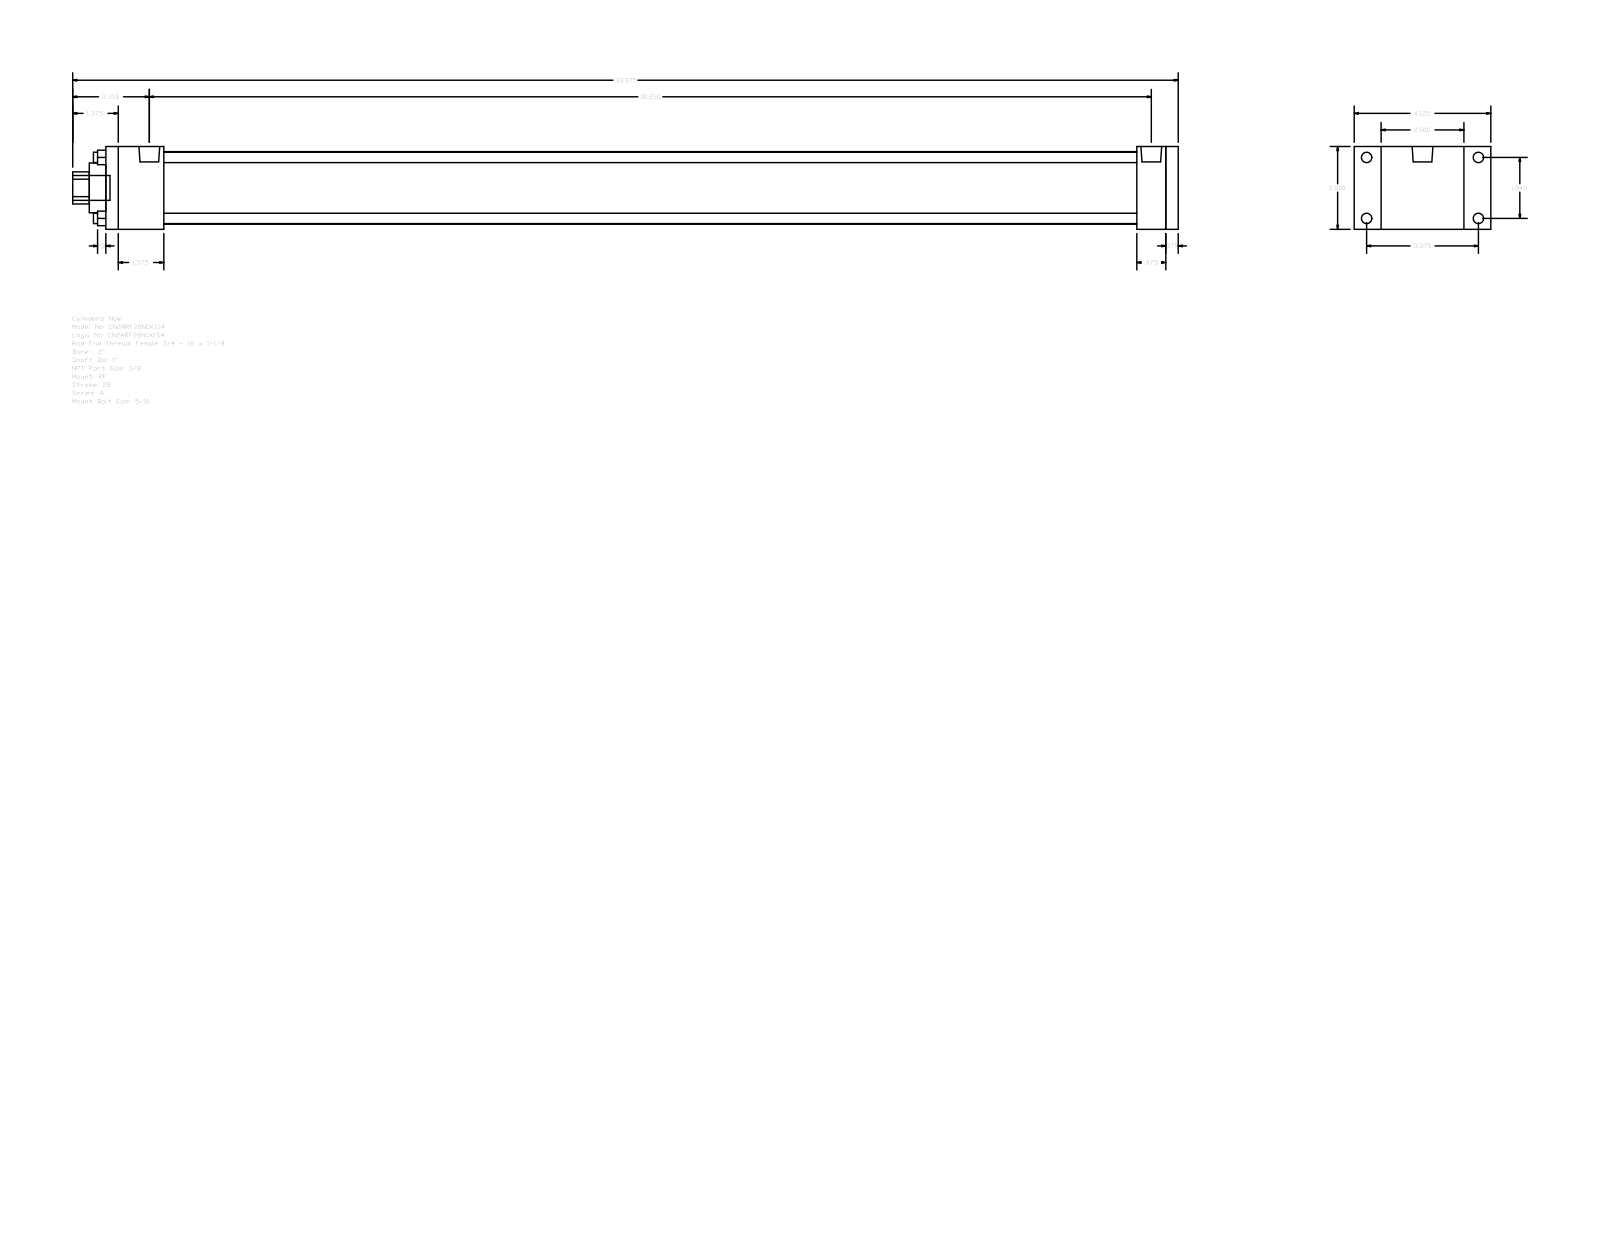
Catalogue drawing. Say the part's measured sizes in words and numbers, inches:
The part is named "A_RF__0200_1". Its 3-D file was written by "GSSL Pune (CONFIG_CONTROL_DESIGN)". It is 0 solids with 92 faces: 64 planar, 28 cylindrical and 0 other. Overall it measures 33.375 by 4.125 by 2.5 inches. Round holes: 4 of diameter 0.313, 1 of diameter 1, 1 of diameter 1.5, 1 of diameter 2.19. Round bosses or shafts: 4 of diameter 0.313, 4 of diameter 0.219, 2 of diameter 0.627, 1 of diameter 0.75. Partial cylindrical surfaces (rounded edges, fillets, slot ends): 1 of radius 0.484. The main face-to-face distances are 2.5, 0.375, 32.375, 32, 0.813, 1.75, 30.25, 30.625, 31.125, 29.375. The hole center spacings are 1.301, 1.84, 2.602.
